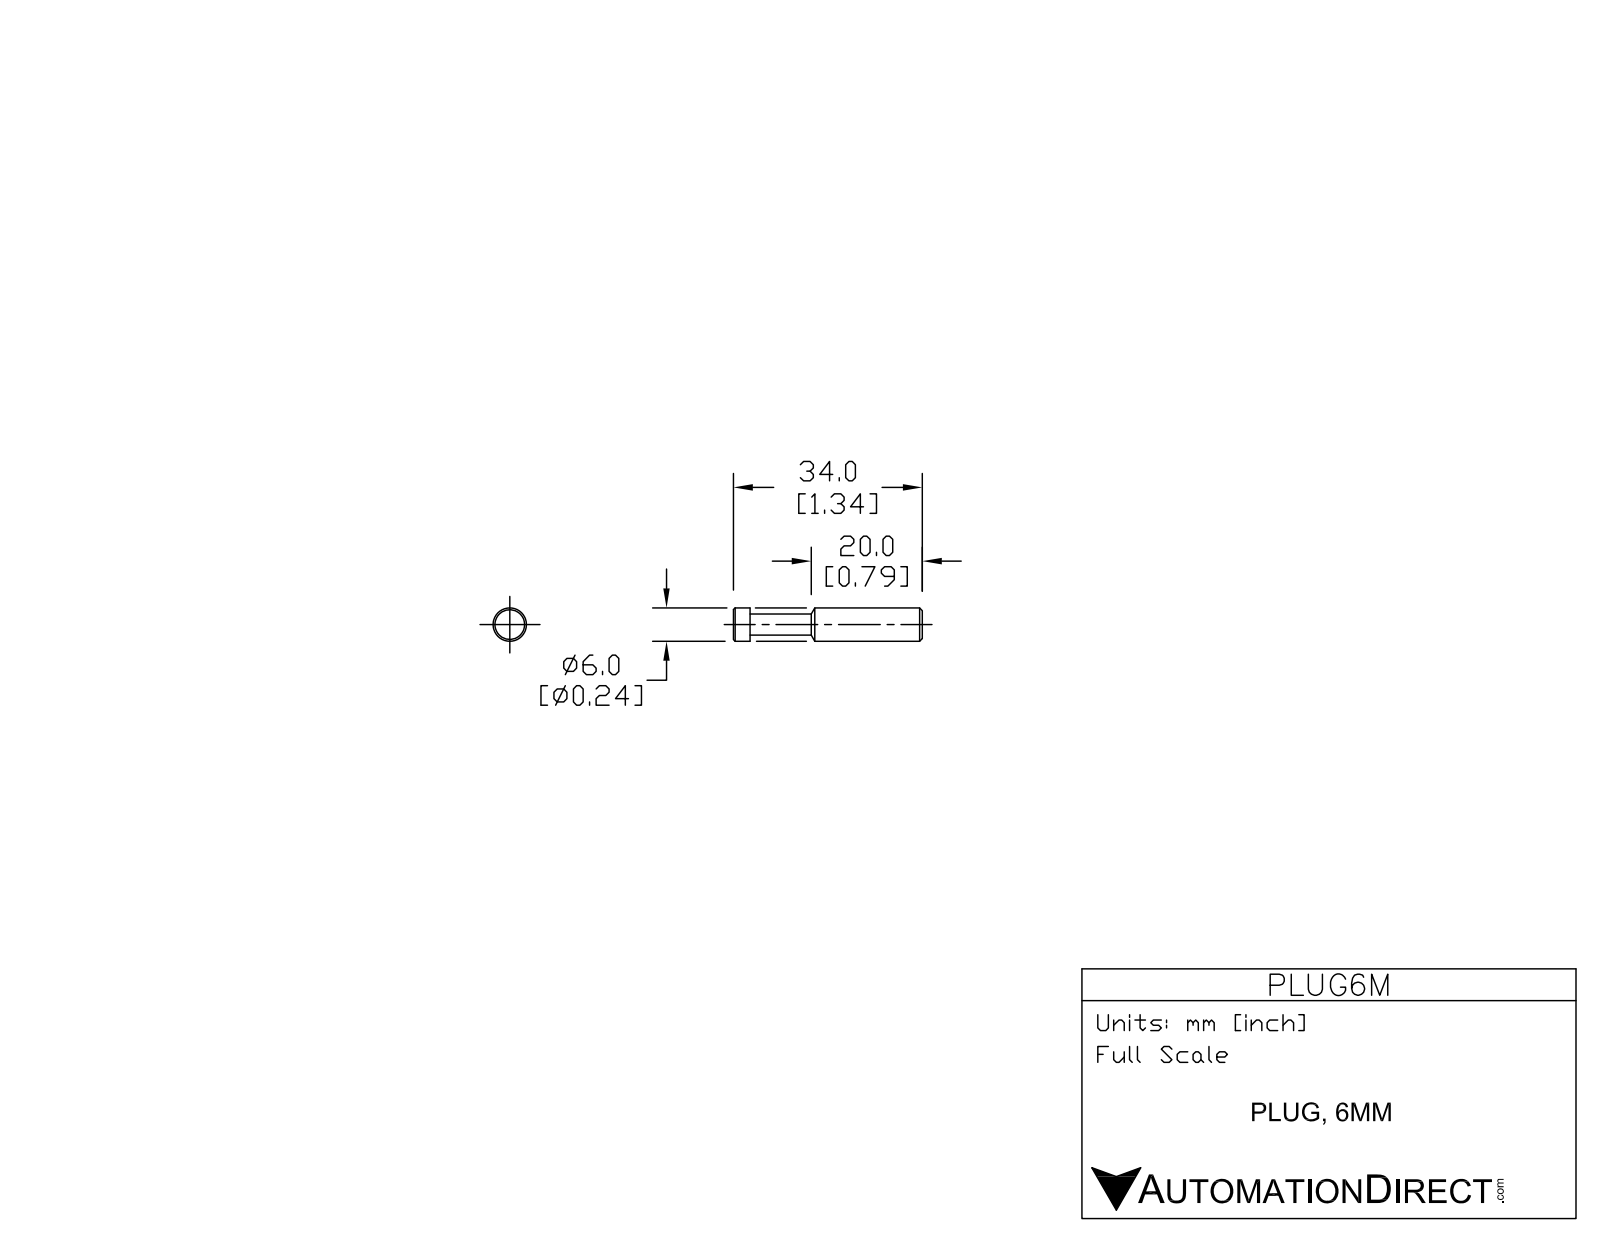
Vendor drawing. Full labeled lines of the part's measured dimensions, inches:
Part name (STEP PRODUCT): PLUG6M
STEP written by: SolidWorks 2015 (AUTOMOTIVE_DESIGN)
Units: inches
Bodies: 1 solid, 15 faces (3 planar, 6 cylindrical, 6 other)
Overall size (bounding box): 1.339 × 0.236 × 0.236
Volume: 0.047 in³ · Surface area: 0.987 in²
Round bosses / shafts (diameter × count): ⌀0.236 ×1, ⌀0.15 ×1
Main face-to-face distances: 1.339, 0.118, 1.22
